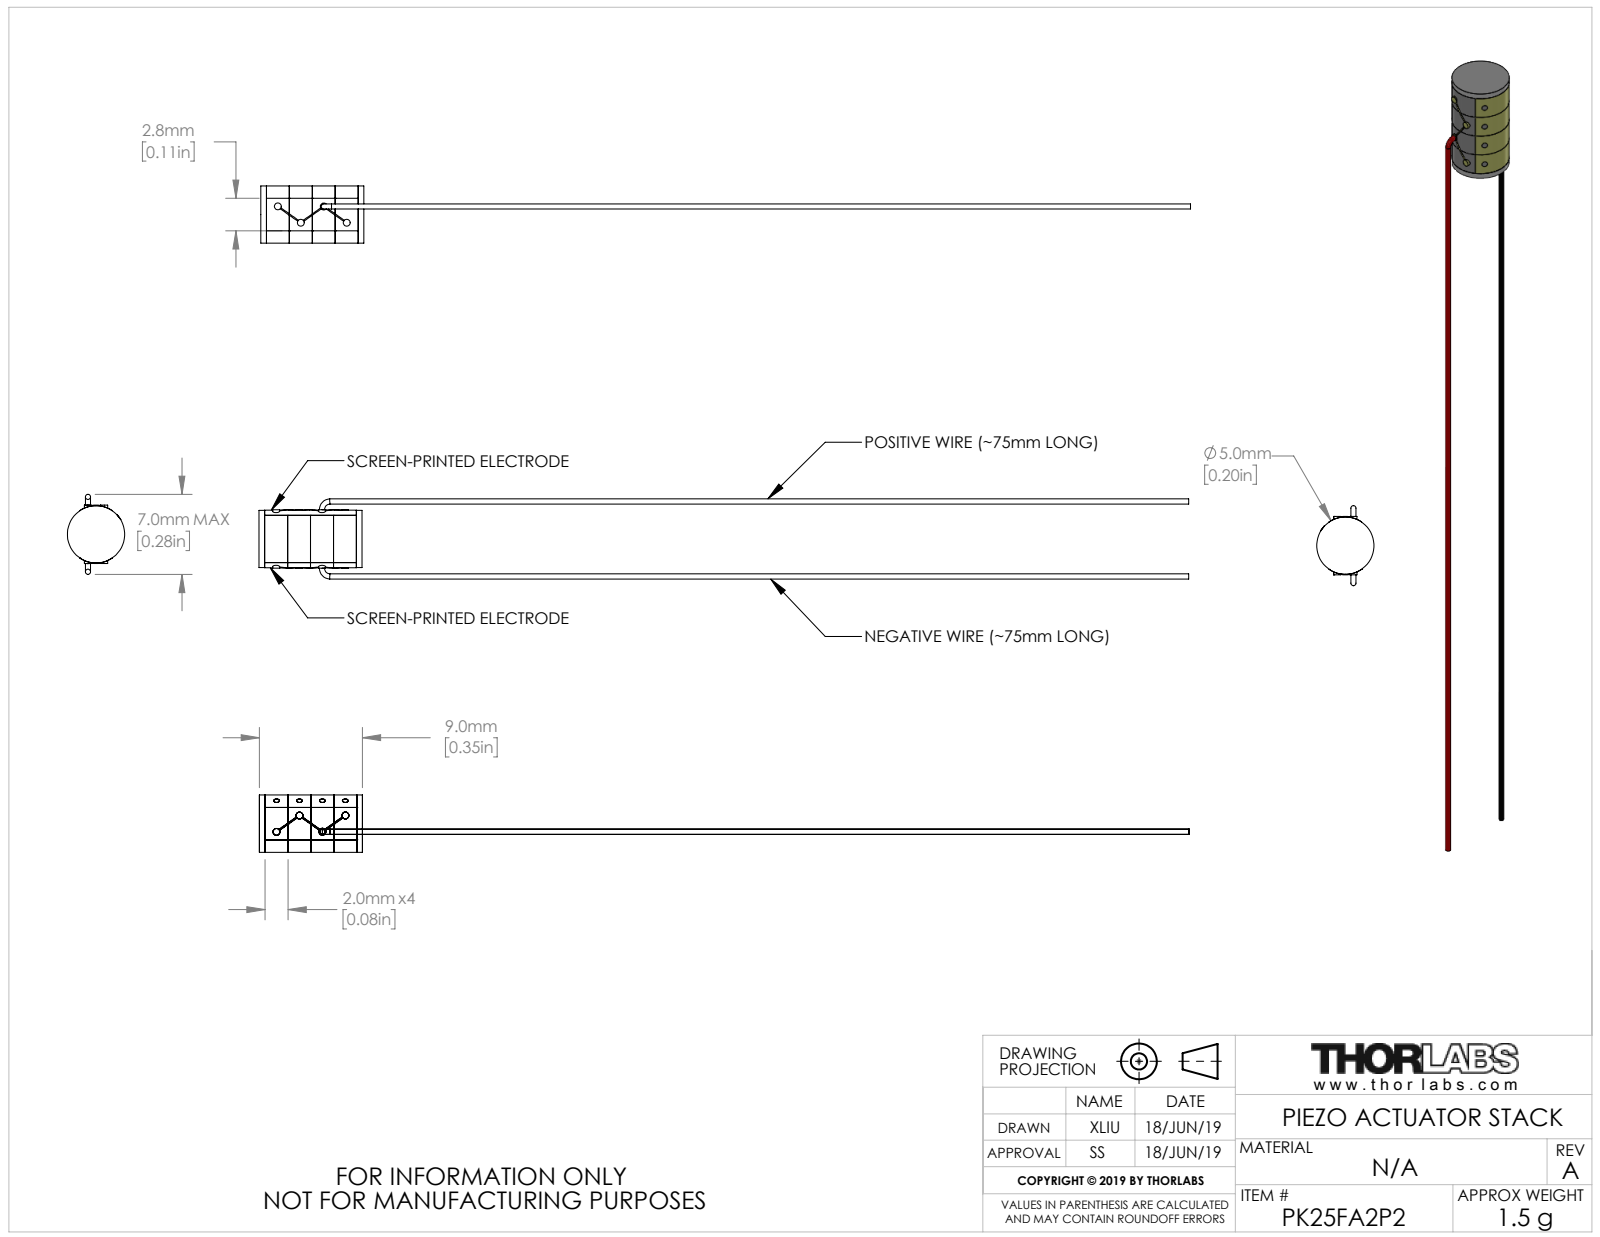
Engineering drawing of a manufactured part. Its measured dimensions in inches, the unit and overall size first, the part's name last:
Units: inches
Overall size (bounding box): 3.196 × 0.275 × 0.197
Round bosses / shafts (diameter × count): ⌀0.024 ×4, ⌀0.02 ×4, ⌀0.018 ×2, ⌀0.197 ×1
Partial cylindrical surfaces — rounded edges, fillets, slot ends (radius × count): R0.099 ×1
Main face-to-face distances: 0.079, 0.157, 0.236, 0.315, 0.02, 0.098, 0.177, 0.256, 0.335, 0.354
Volume: 0.012 in³ · Surface area: 0.927 in²
Bodies: 7 solids, 122 faces (42 planar, 56 cylindrical, 24 other)
Part name (STEP PRODUCT): CTN014121
STEP written by: SolidWorks 2018 (AUTOMOTIVE_DESIGN)
